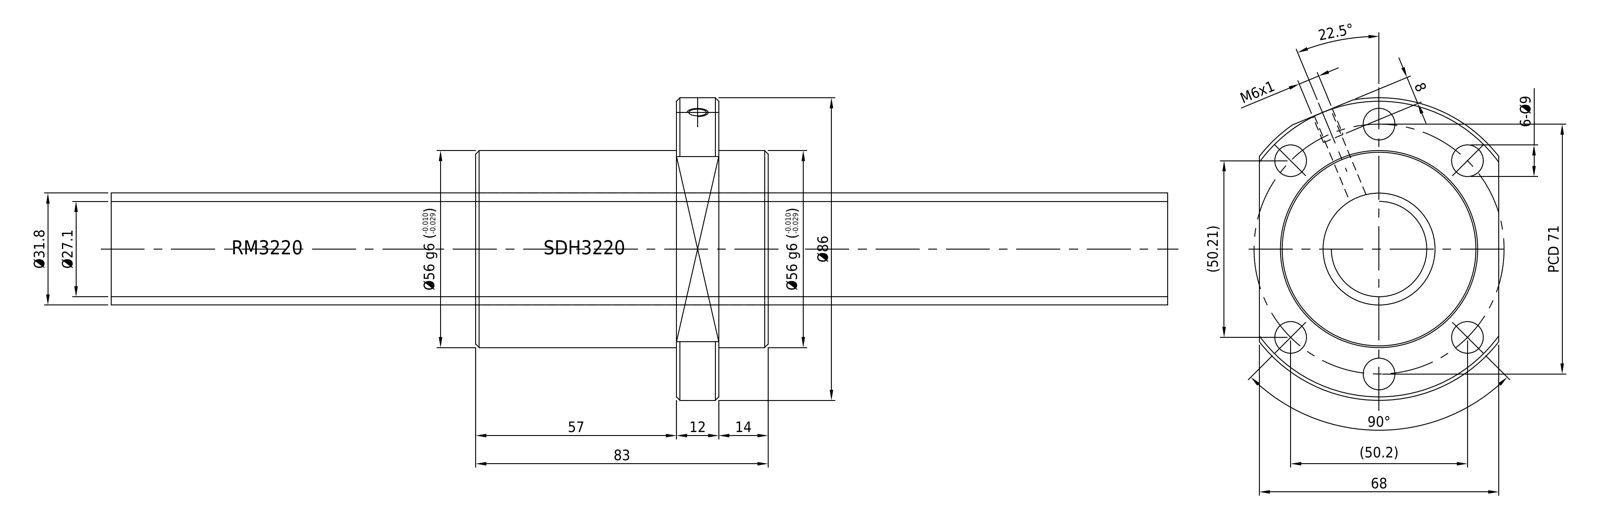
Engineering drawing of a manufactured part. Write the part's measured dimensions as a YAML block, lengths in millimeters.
part_name: "SDH3220; RM3220"
step_written_by: "SolidWorks 2013 (CONFIG_CONTROL_DESIGN)"
units: millimeters
bodies: {solids: 2, faces: 48, planar: 9, cylindrical: 27, other: 12}
overall_size: [300, 86, 68]
volume: 400204
surface_area: 65430
round_holes:
  - {diameter: 9, count: 6}
  - {diameter: 3, count: 1}
  - {diameter: 5, count: 1}
  - {diameter: 32, count: 1}
round_bosses_or_shafts:
  - {diameter: 56, count: 1}
  - {diameter: 31.6, count: 1}
partial_cylinders:
  - {radius: 43, count: 1}
face_to_face_distances: [12, 69, 57, 14, 26, 83, 108.5, 191.5, 122.5, 134.5]
hole_center_spacings: [35.5, 71, 27.17, 27.18, 50.2, 50.21, 65.59, 65.6]
